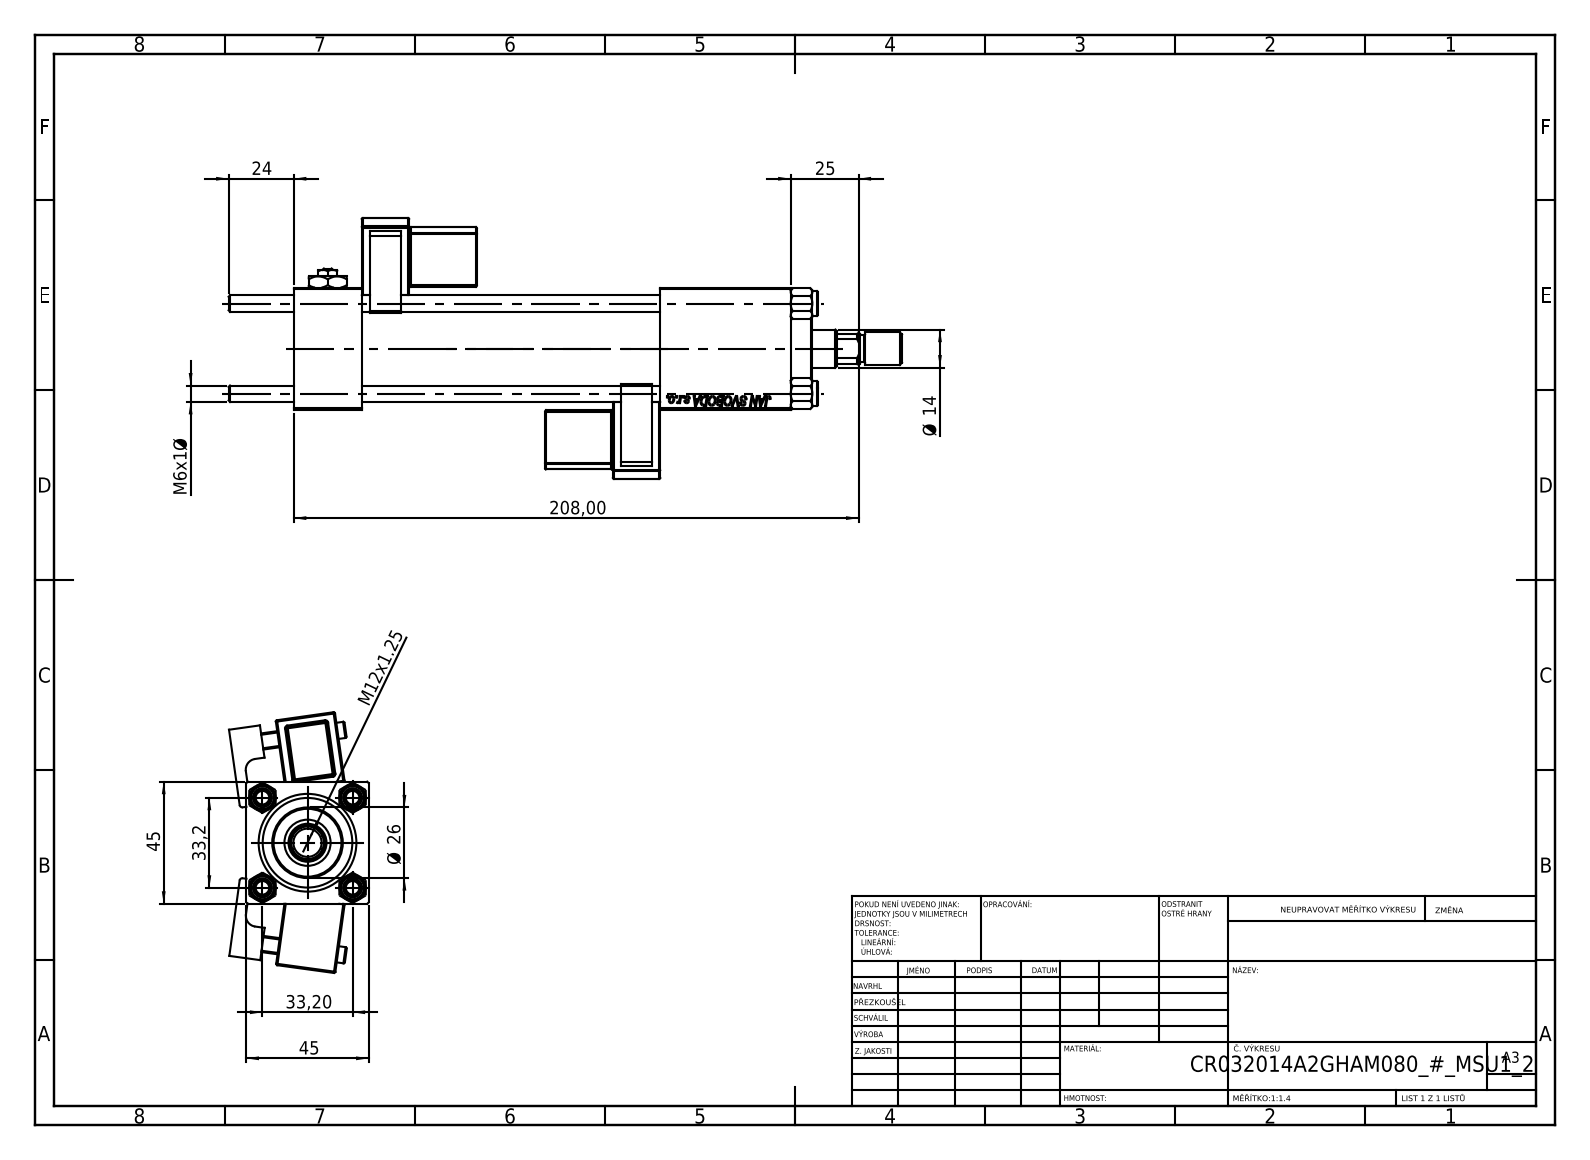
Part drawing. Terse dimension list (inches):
name: NUT_M5; V215CR_MSU; Zatka_pro_OIL_PORT; V215_VC_A (+4 more)
written by: SolidWorks 2019 (CONFIG_CONTROL_DESIGN)
unit: in
bodies: 15 solids, 1356 faces (608 planar, 148 cylindrical, 600 other)
size: 9.764 × 3.781 × 2.024
volume: 16.82 in³; area: 166 in²
holes: 4× ⌀0.236, 2× ⌀0.276, 2× ⌀0.518, 2× ⌀0.787, 1× ⌀0.256, 1× ⌀0.551, 1× ⌀0.669, 1× ⌀0.945, 1× ⌀1.26, 1× ⌀1.299
bosses: 4× ⌀0.354, 2× ⌀0.236, 1× ⌀1.496, 1× ⌀1.024, 1× ⌀0.472, 1× ⌀0.394
rounds: 48× R0.02, 2× R0.039, 2× R0.098, 2× R0.157, 1× R0.256
face distances: 1.772, 0.984, 0.118, 5.315, 4.331, 7.205, 6.22, 1.89, 0.591, 3.642
hole spacings: 0.924, 1.307, 1.848, 5.335
